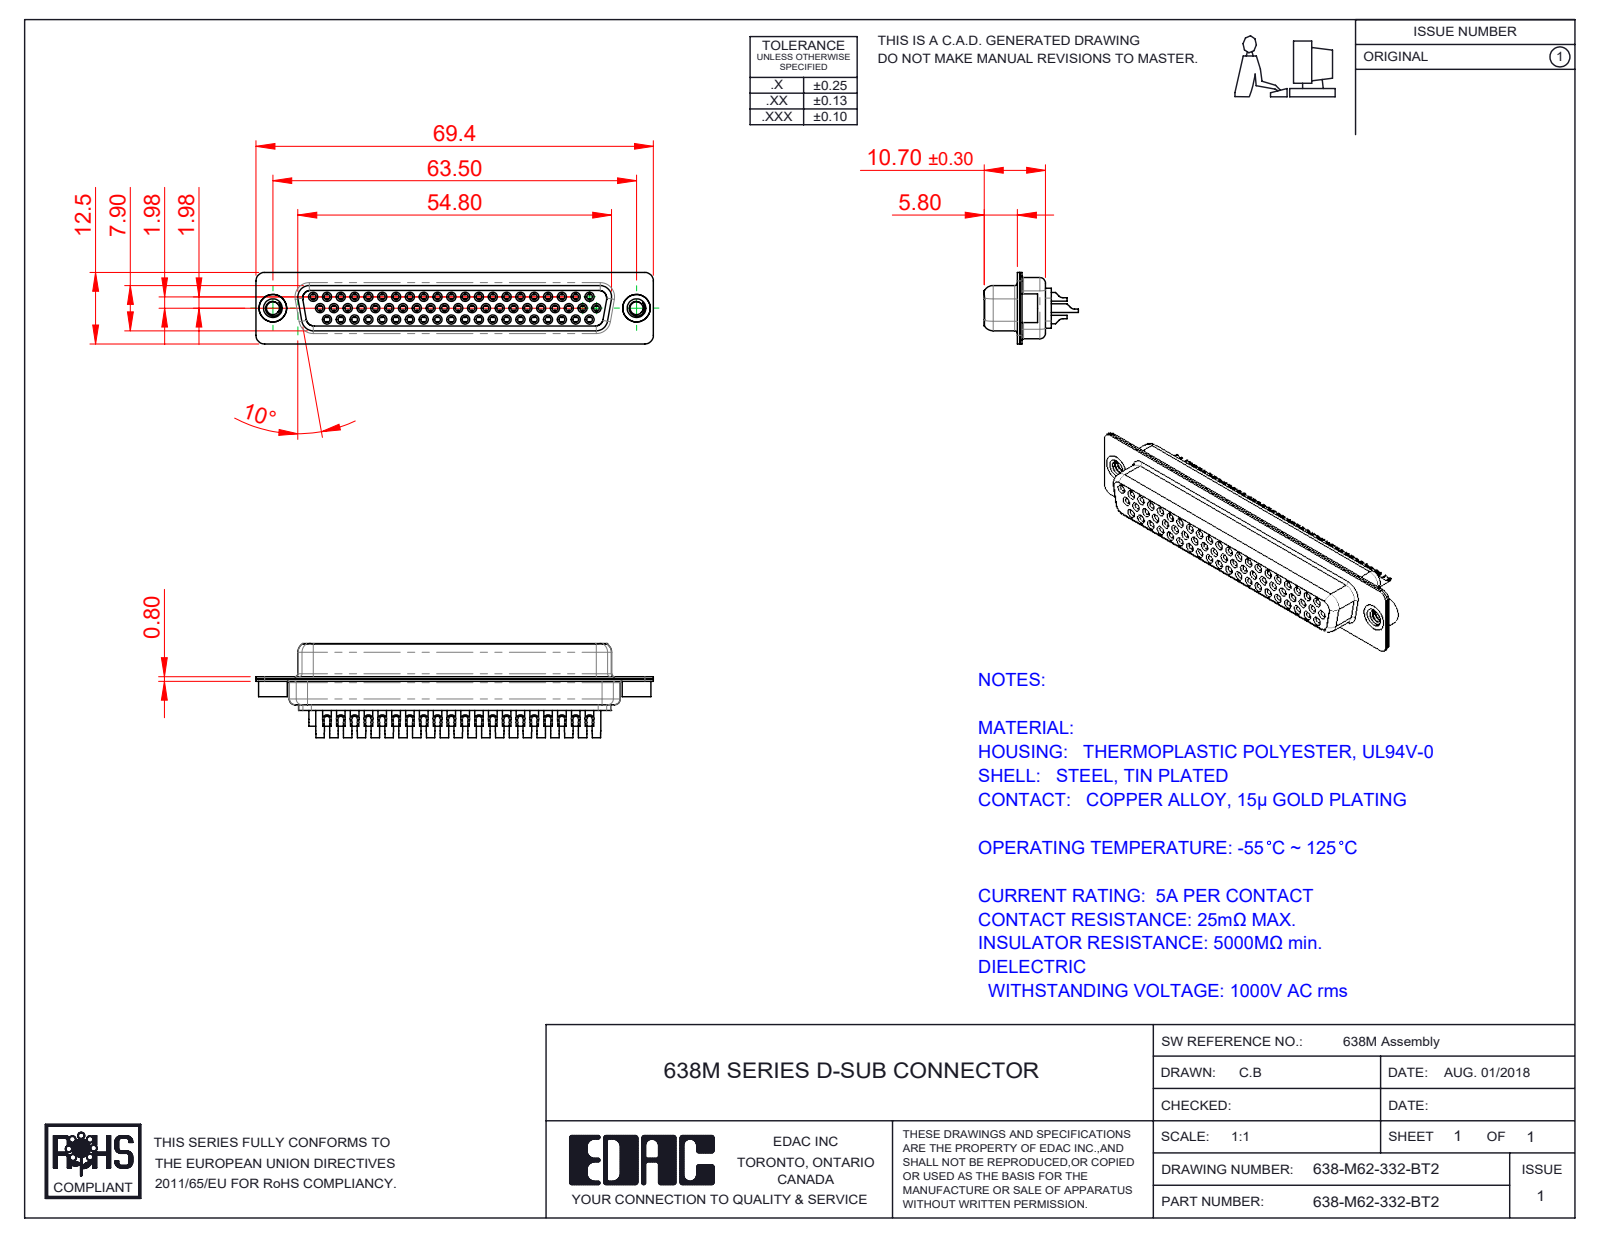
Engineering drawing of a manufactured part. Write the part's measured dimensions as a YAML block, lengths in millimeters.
part_name: "638M Contact Row 2_32; 638M Contact Row 1_32; 638M 4-40 Threaded Rivet; 638-M62-332-BT2 (+4 more)"
step_written_by: "SolidWorks 2020 (CONFIG_CONTROL_DESIGN)"
units: millimeters
bodies: {solids: 67, faces: 3689, planar: 1121, cylindrical: 1439, other: 1129}
overall_size: [69.4, 16.45, 12.5]
volume: 5074
surface_area: 16874
round_holes:
  - {diameter: 1, count: 62}
  - {diameter: 1.1, count: 62}
  - {diameter: 1.7, count: 62}
  - {diameter: 1.8, count: 62}
  - {diameter: 2, count: 62}
  - {diameter: 2.26, count: 2}
  - {diameter: 4, count: 2}
  - {diameter: 4.8, count: 2}
round_bosses_or_shafts:
  - {diameter: 2.2, count: 62}
  - {diameter: 1.6, count: 62}
  - {diameter: 1.5, count: 62}
  - {diameter: 5, count: 2}
  - {diameter: 4.9, count: 2}
partial_cylinders:
  - {radius: 1.5, count: 16}
  - {radius: 2, count: 12}
  - {radius: 1.35, count: 8}
  - {radius: 1.6, count: 8}
  - {radius: 1, count: 7}
  - {radius: 0.25, count: 4}
  - {radius: 0.5, count: 4}
  - {radius: 0.6, count: 4}
face_to_face_distances: [0.4, 1.4, 0.45, 8.45, 8.9, 1, 1.8, 6.2, 7.05, 1.85]
hole_center_spacings: [7.24, 2.32, 2.41, 4.13, 9.65, 4.83, 14.48, 16.89]
